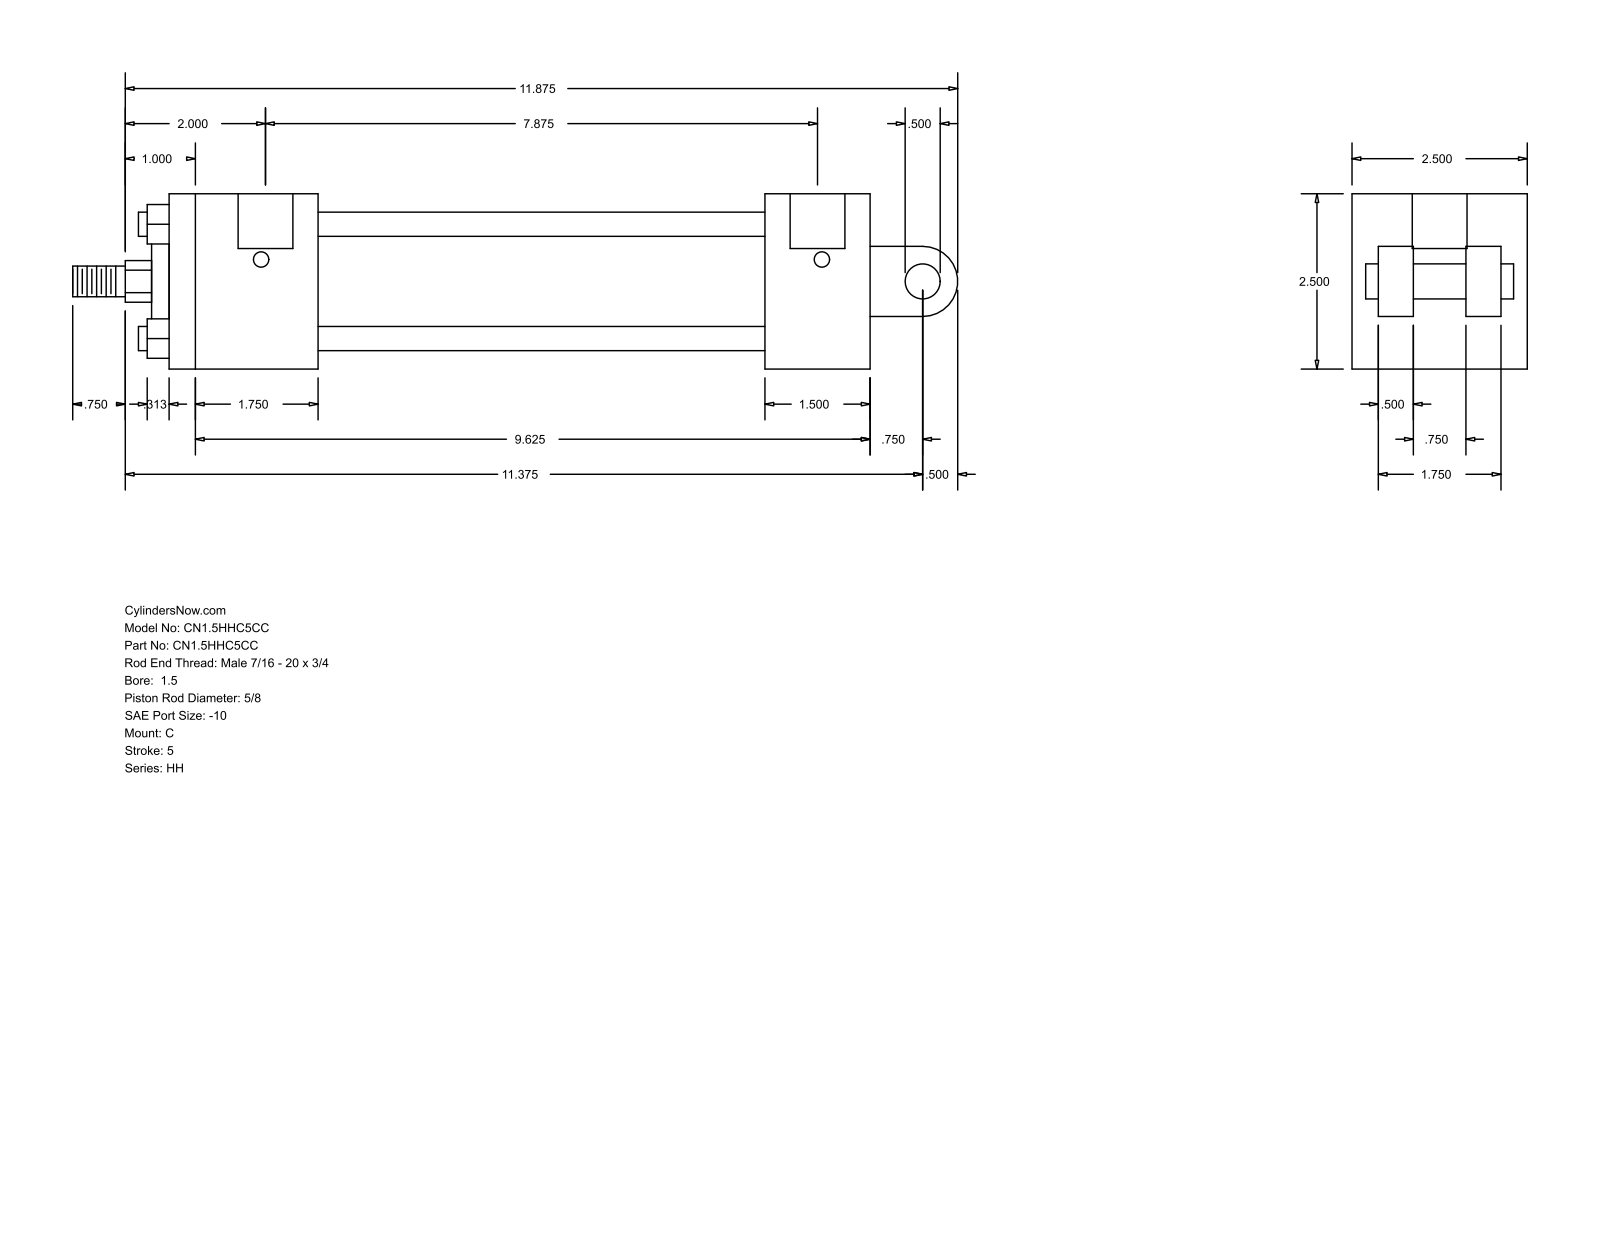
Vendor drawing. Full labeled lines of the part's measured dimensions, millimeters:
Part name (STEP PRODUCT): HH_C__0150_0.625
STEP written by: GSSL Pune (CONFIG_CONTROL_DESIGN)
Units: millimetres
Bodies: 0 solids, 99 faces (70 planar, 29 cylindrical, 0 other)
Overall size (bounding box): 320.68 × 63.5 × 63.5
Round holes (diameter × count): ⌀5.56 ×4, ⌀19.84 ×2
Round bosses / shafts (diameter × count): ⌀8.76 ×4, ⌀44.45 ×1, ⌀28.57 ×1, ⌀15.88 ×1, ⌀12.7 ×1, ⌀11.11 ×1
Partial cylindrical surfaces — rounded edges, fillets, slot ends (radius × count): R7.54 ×1, R12.7 ×1
Main face-to-face distances: 63.5, 254, 38.1, 53.97, 215.9, 161.93, 200.03, 12.7, 19.05, 22.22
Hole centre spacings: 1.59, 201.61, 203.2, 200.02
